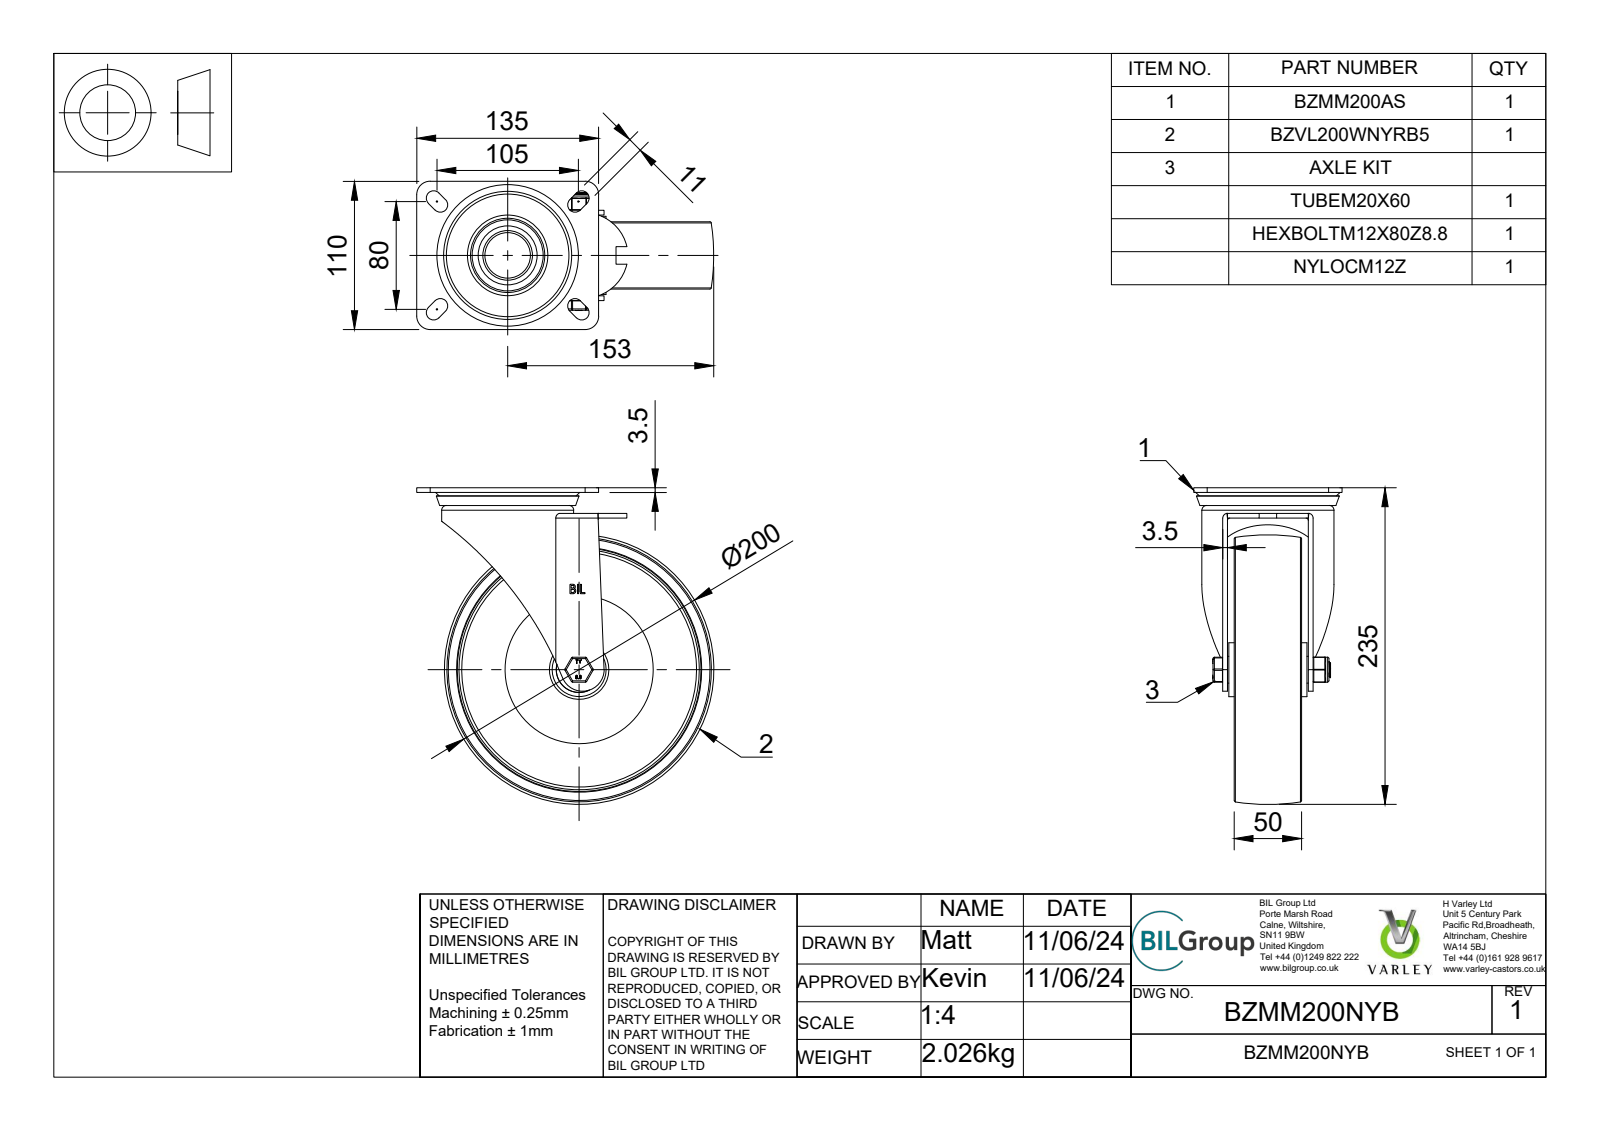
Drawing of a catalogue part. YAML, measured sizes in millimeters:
part_name: "BZMM200NYB v4; BZMM200AS - 2 v2; ZINC PLATED, PRESSED STEEL TOP PLATE; ZINC PLATED, PRESSED STEEL TOP PLATE Geometry (+7 more)"
step_written_by: "Autodesk Translation Framework v13.14.0.145 (AUTOMOTIVE_DESIGN)"
units: millimeters
bodies: {solids: 58, faces: 516, planar: 226, cylindrical: 147, other: 143}
overall_size: [235, 220.5, 110]
volume: 780604
surface_area: 263966
round_holes:
  - {diameter: 12, count: 1}
  - {diameter: 12.2, count: 1}
  - {diameter: 12.5, count: 1}
  - {diameter: 14, count: 1}
  - {diameter: 20, count: 1}
  - {diameter: 20.2, count: 1}
  - {diameter: 33.75, count: 1}
  - {diameter: 55, count: 1}
  - {diameter: 91, count: 1}
round_bosses_or_shafts:
  - {diameter: 7.5, count: 8}
  - {diameter: 98, count: 1}
  - {diameter: 78, count: 1}
  - {diameter: 50, count: 1}
  - {diameter: 40, count: 1}
  - {diameter: 39.75, count: 1}
  - {diameter: 34, count: 1}
  - {diameter: 19.9, count: 1}
partial_cylinders:
  - {radius: 0.5, count: 18}
  - {radius: 1, count: 12}
  - {radius: 5.5, count: 8}
  - {radius: 1.75, count: 4}
  - {radius: 10, count: 4}
  - {radius: 3.5, count: 2}
  - {radius: 32.45, count: 2}
  - {radius: 13.5, count: 1}
face_to_face_distances: [3.5, 9.5, 55, 5, 28.75, 38.25, 63.5, 25.25, 34.75, 9]
